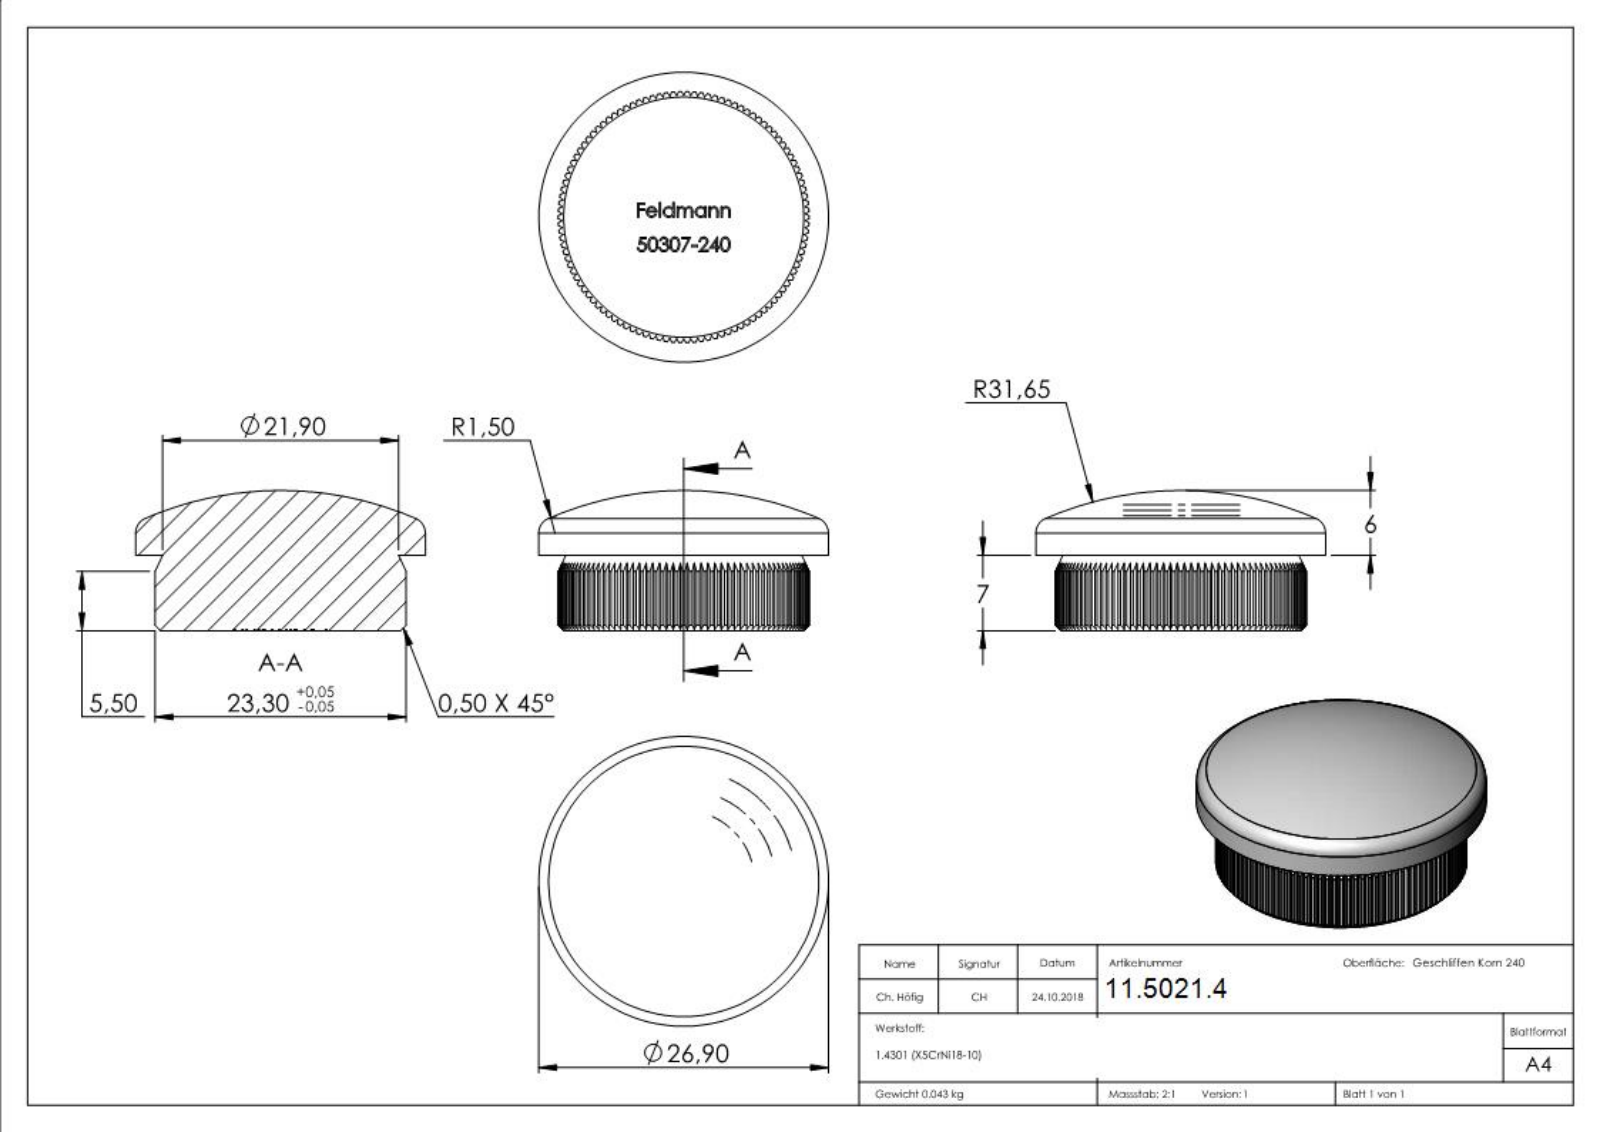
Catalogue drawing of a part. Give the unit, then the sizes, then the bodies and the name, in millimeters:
Units: millimetres
Overall size (bounding box): 26.9 × 26.9 × 13
Round bosses / shafts (diameter × count): ⌀26.9 ×1
Partial cylindrical surfaces — rounded edges, fillets, slot ends (radius × count): R11.65 ×1
Main face-to-face distances: 11.3, 7, 11.32, 11.28, 6.9, 2.97, 0.39, 1.4, 3.39, 3.19
Volume: 5 454 mm³ · Surface area: 2 198 mm²
Bodies: 1 solid, 564 faces (341 planar, 112 cylindrical, 111 other)
Part name (STEP PRODUCT): 50307-240
STEP written by: SolidWorks 2015 (CONFIG_CONTROL_DESIGN)
